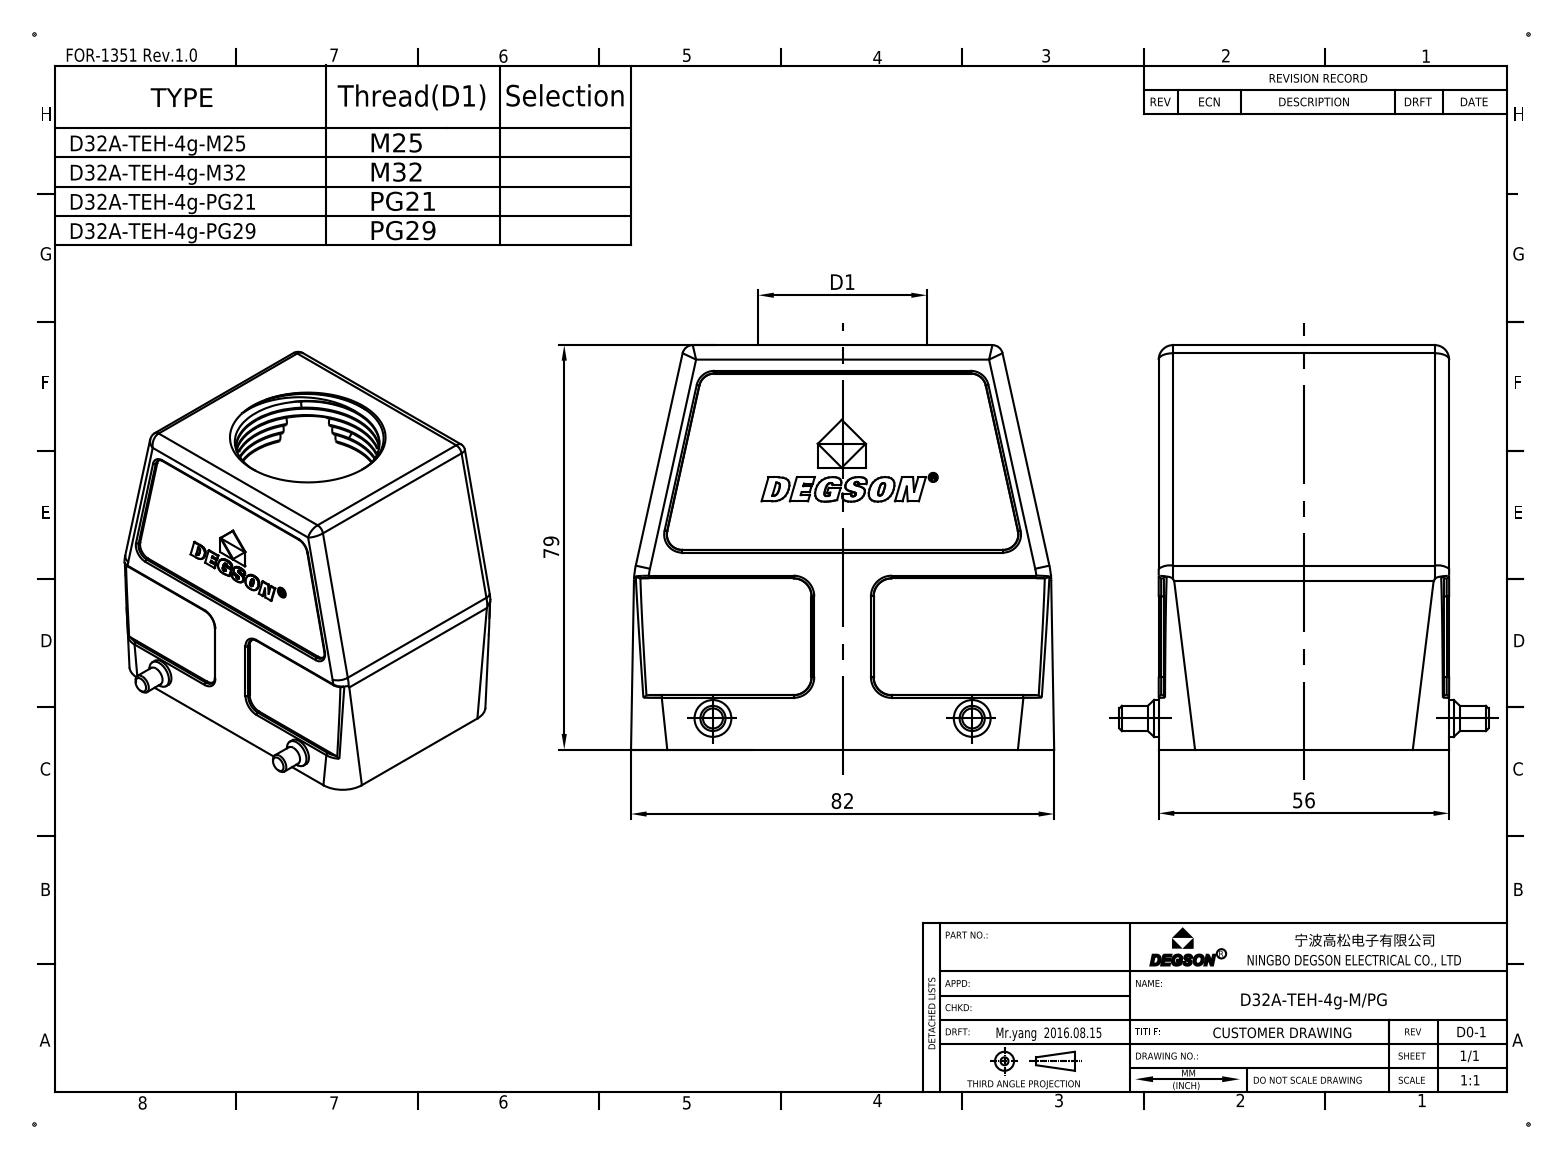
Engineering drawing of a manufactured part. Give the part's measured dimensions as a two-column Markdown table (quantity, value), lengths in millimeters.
| quantity | value |
| --- | --- |
| part name | D32A-TEH-4G-MPG |
| STEP written by | CREO PARAMETRIC BY PTC INC, 2018100 (CONFIG_CONTROL_DESIGN) |
| units | millimeters |
| bodies | 1 solid, 161 faces (49 planar, 68 cylindrical, 44 other) |
| overall size | 81.5 × 78.5 × 70.8 |
| volume | 102 644 mm³ |
| surface area | 44 583 mm² |
| round holes (diameter × count) | 2.8 × 8, 30.5 × 1 |
| round bosses / shafts (diameter × count) | 7 × 2, 4.95 × 2, 3.2 × 2 |
| partial cylindrical surfaces (radius × count) | 1 × 16, 3 × 4, 25 × 2 |
| main face-to-face distances | 2, 52, 50, 3, 10.7, 54, 60.1, 70.8, 55, 1 |
| hole center spacings | 15.98, 24.02, 33.24, 38.59, 66, 67.91, 70.24, 8.04 |
